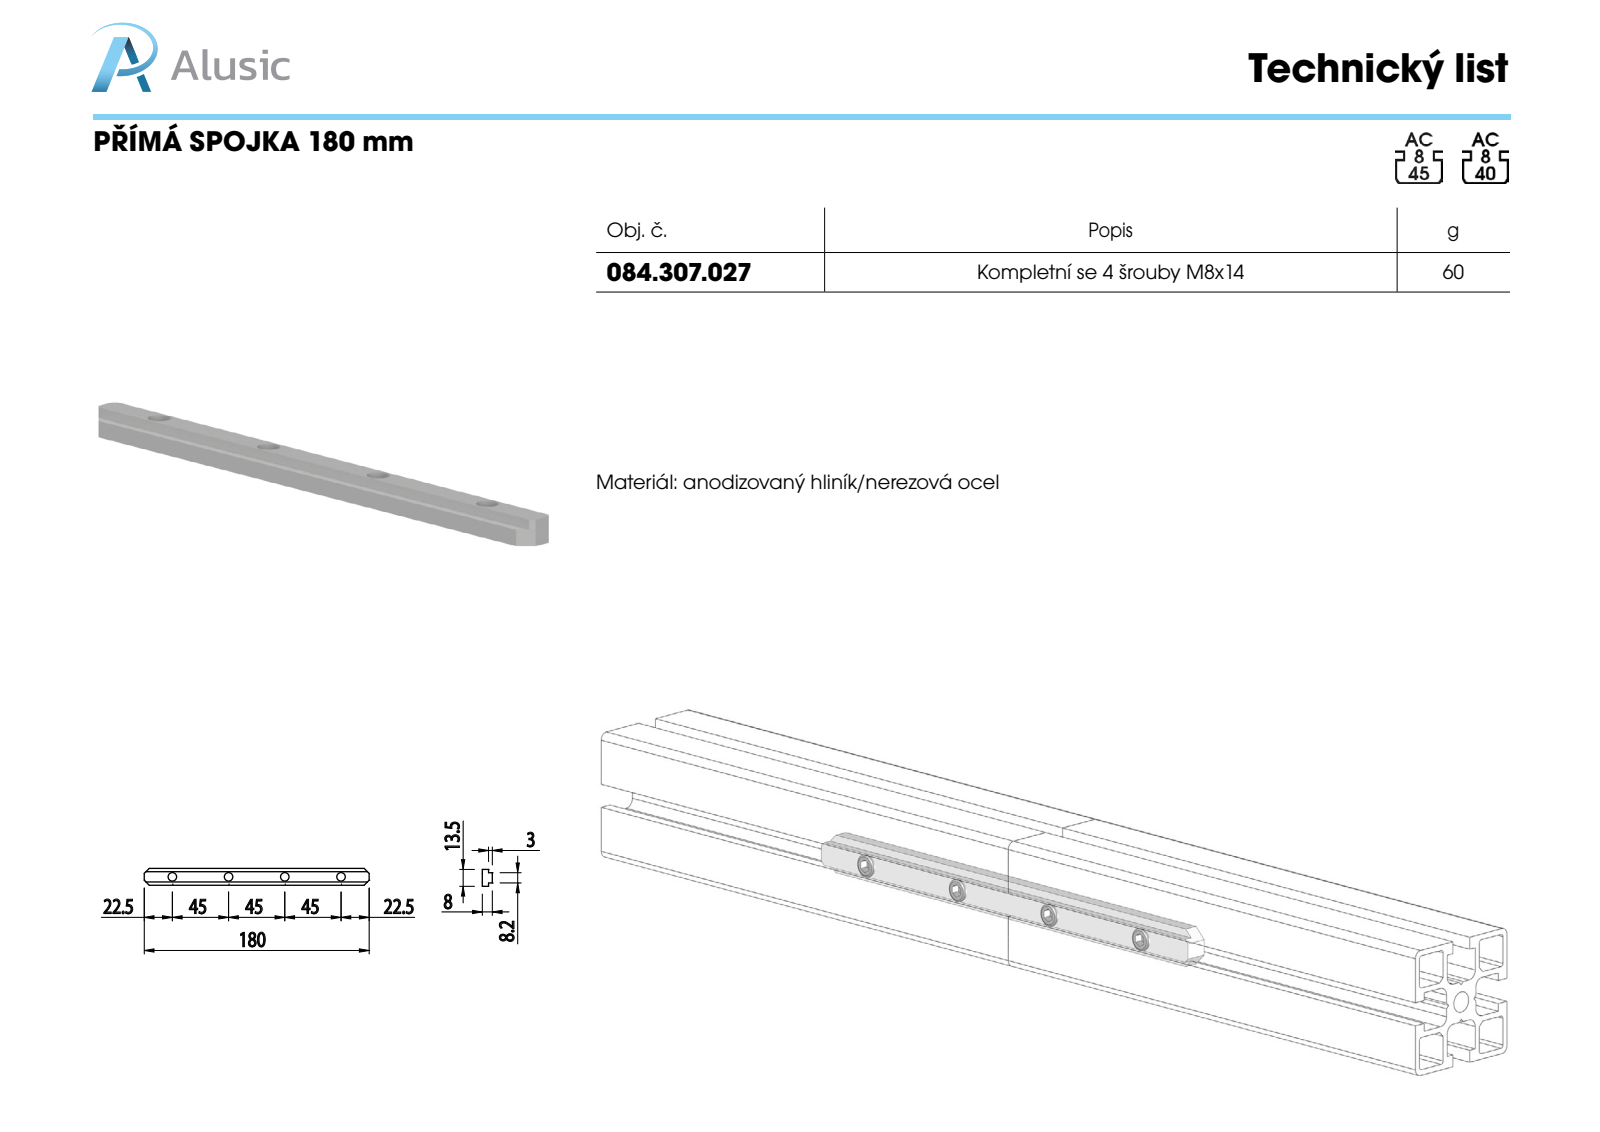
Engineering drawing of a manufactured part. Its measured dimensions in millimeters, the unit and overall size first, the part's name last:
Units: millimetres
Overall size (bounding box): 180 × 13.5 × 8
Round holes (diameter × count): ⌀6.8 ×4
Main face-to-face distances: 8, 2.65, 10.85, 5, 3, 13.5, 8.2, 131.14, 180
Hole centre spacings: 45, 90, 135
Volume: 15 245 mm³ · Surface area: 8 197 mm²
Bodies: 1 solid, 22 faces (14 planar, 8 cylindrical, 0 other)
Part name (STEP PRODUCT): 084.307.027
STEP written by: SolidWorks 2011 (CONFIG_CONTROL_DESIGN)
